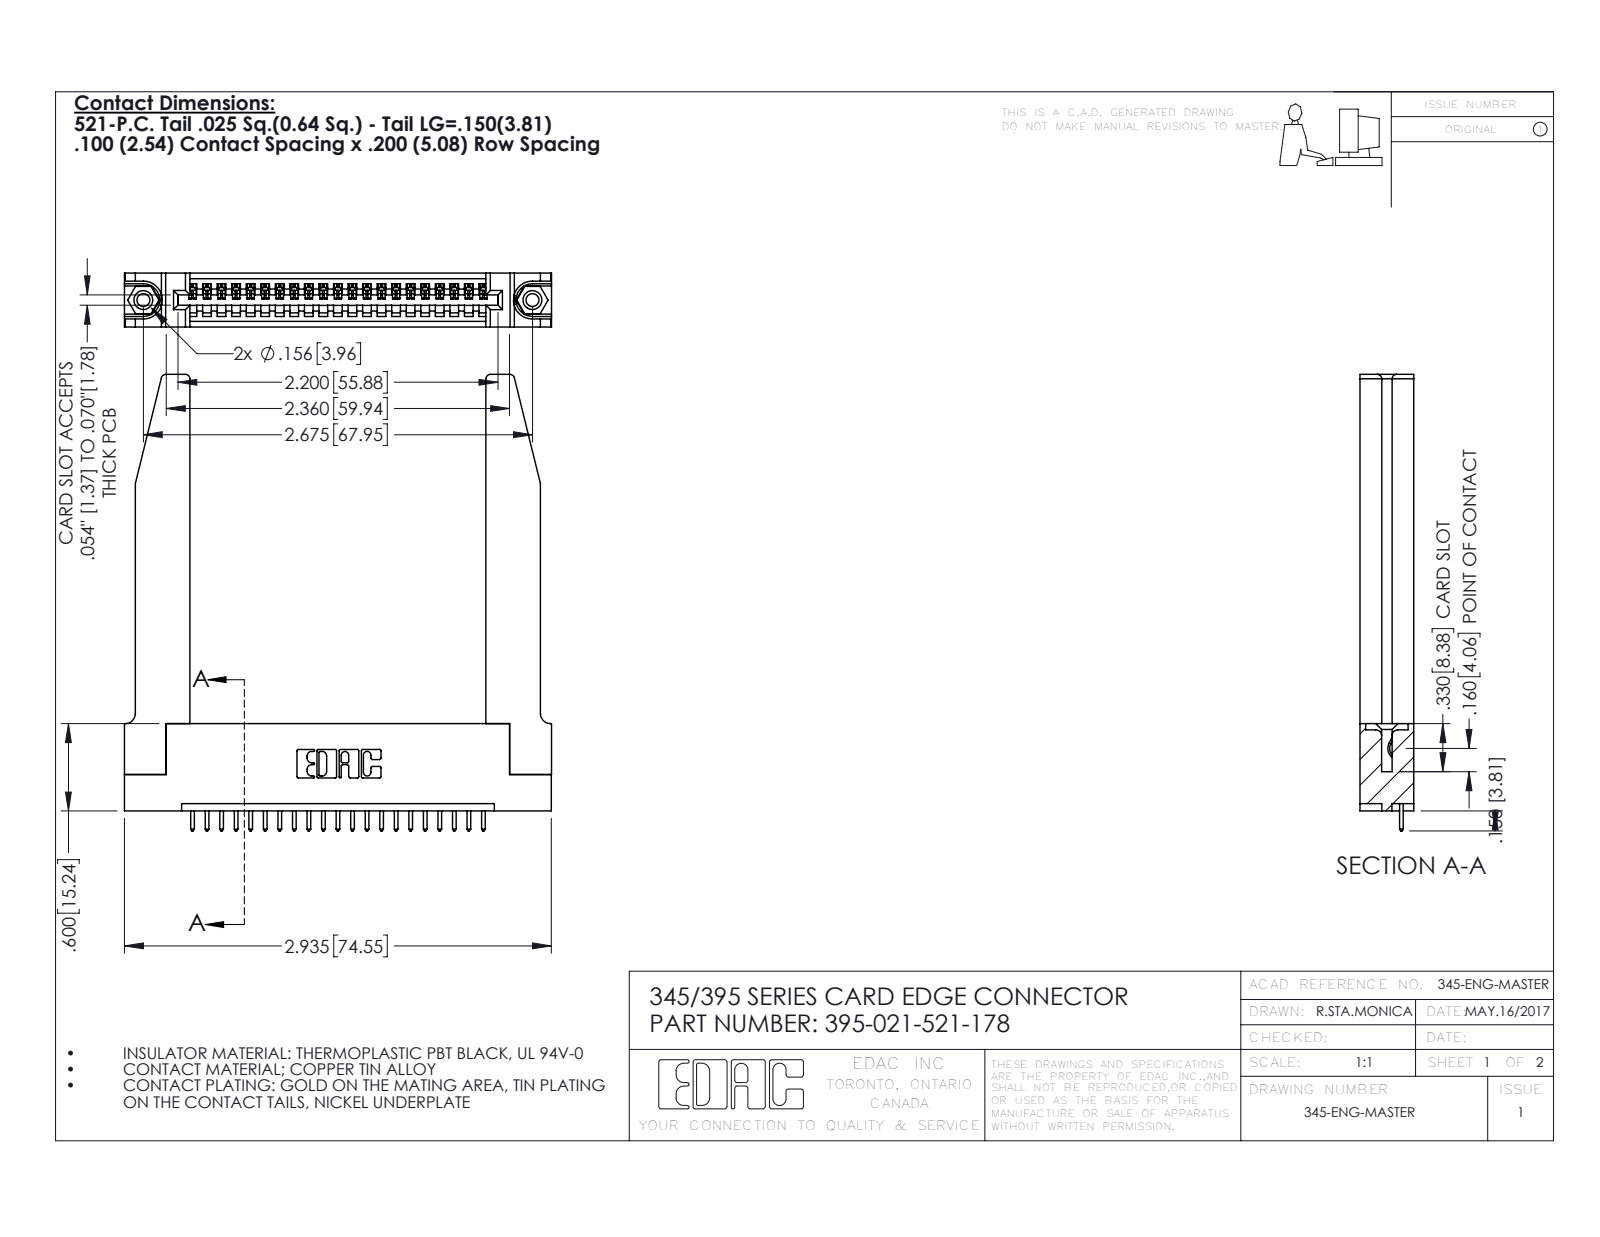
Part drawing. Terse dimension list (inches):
name: 395-021-521-178; 345-250-001_345-250-001-102; 345-220-078_345-220-078; 345 Part_Flush Mounting Lugs - 0.156 Dia-TH (+1 more)
written by: SolidWorks 2016 (CONFIG_CONTROL_DESIGN)
unit: in
bodies: 26 solids, 1578 faces (1062 planar, 464 cylindrical, 52 other)
size: 3.137 × 2.936 × 0.37
volume: 0.892 in³; area: 23.92 in²
holes: 2× ⌀0.089, 2× ⌀0.125, 2× ⌀0.156, 1× ⌀0.064
bosses: 2× ⌀0.155
rounds: 42× R0.006, 42× R0.01, 22× R0.01, 8× R0.03, 6× R0.007, 6× R0.031, 3× R0.026, 2× R0.031
face distances: 0.37, 0.072, 0.298, 0.2, 0.098, 0.272, 0.025, 0.15, 0.148, 0.077
hole spacings: 0.27, 2.441, 2.675
